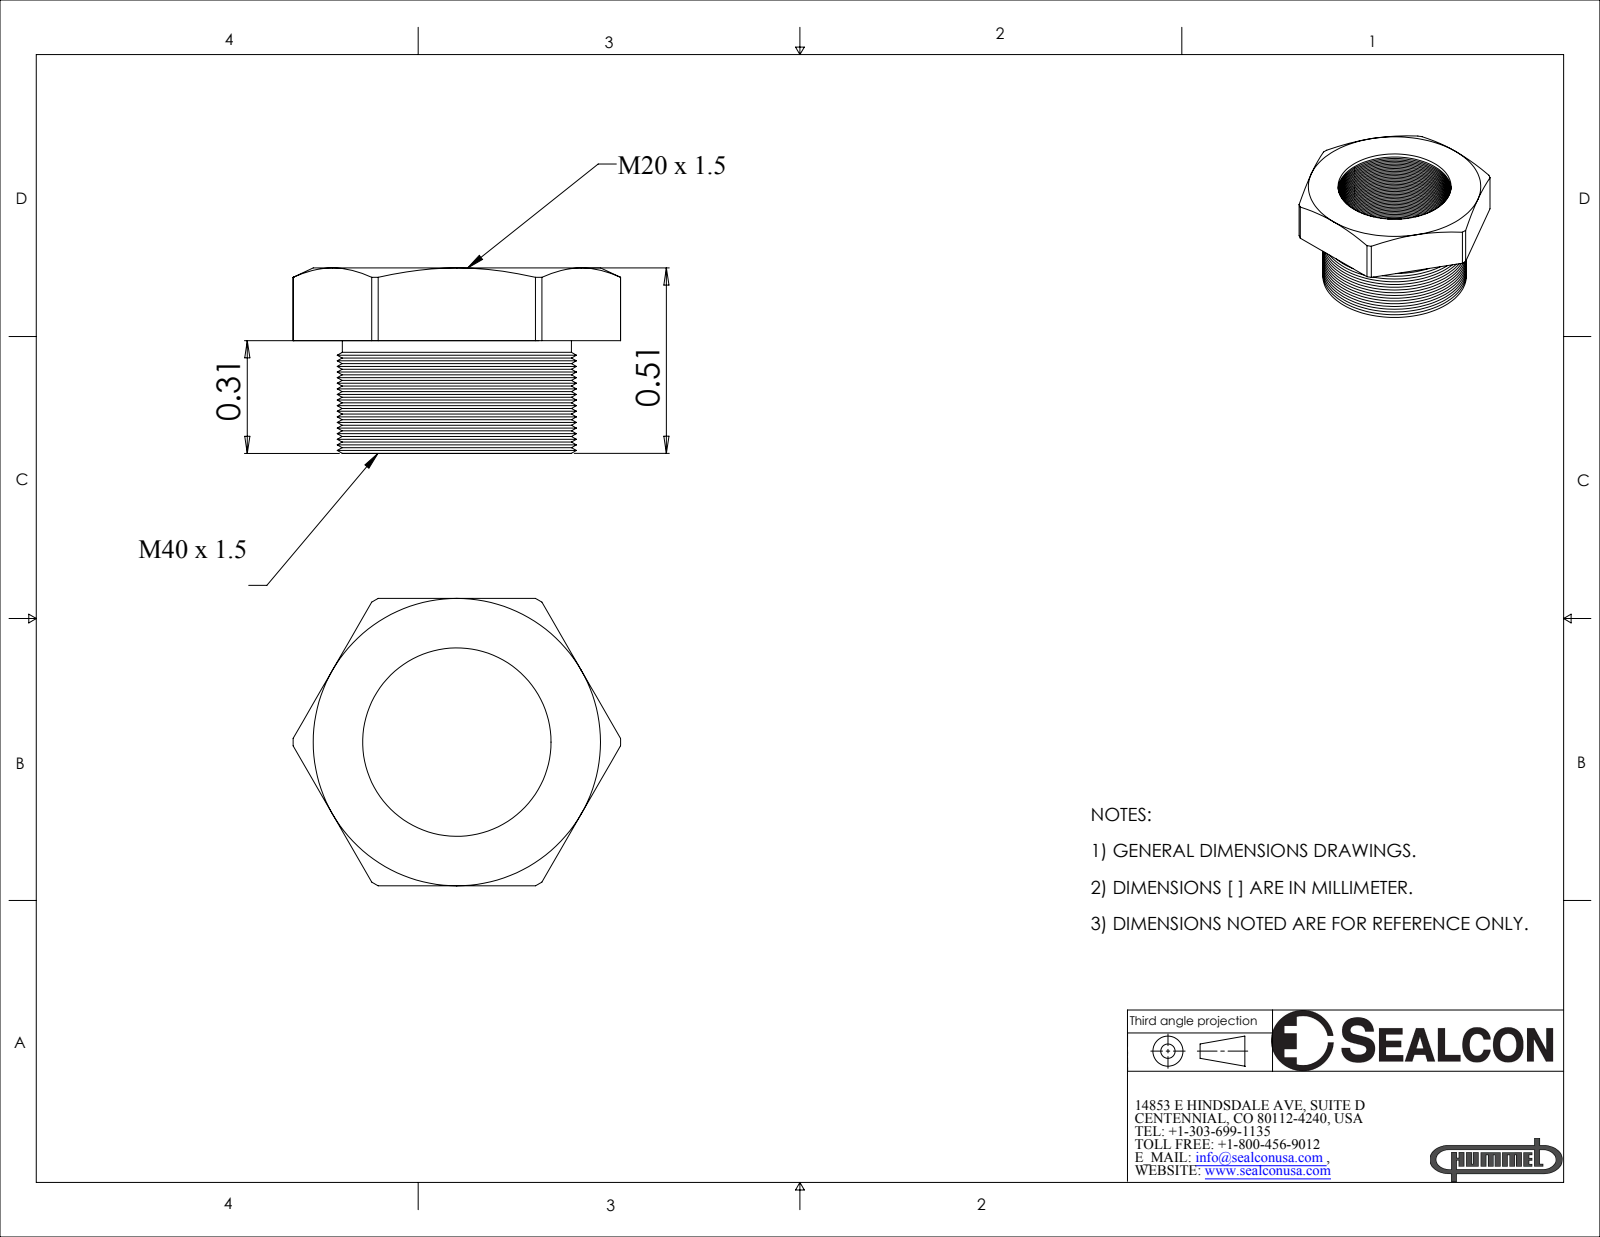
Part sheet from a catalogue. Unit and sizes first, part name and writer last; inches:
Units: inches
Overall size (bounding box): 0.901 × 0.79 × 0.51
Round holes (diameter × count): ⌀0.518 ×1
Round bosses / shafts (diameter × count): ⌀0.63 ×1
Partial cylindrical surfaces — rounded edges, fillets, slot ends (radius × count): R0.45 ×1
Main face-to-face distances: 0.79, 0.2, 0.31, 0.51
Volume: 0.098 in³ · Surface area: 4.047 in²
Bodies: 1 solid, 287 faces (9 planar, 75 cylindrical, 203 other)
Part name (STEP PRODUCT): RM-4020-SS
STEP written by: SolidWorks 2008 (CONFIG_CONTROL_DESIGN)
